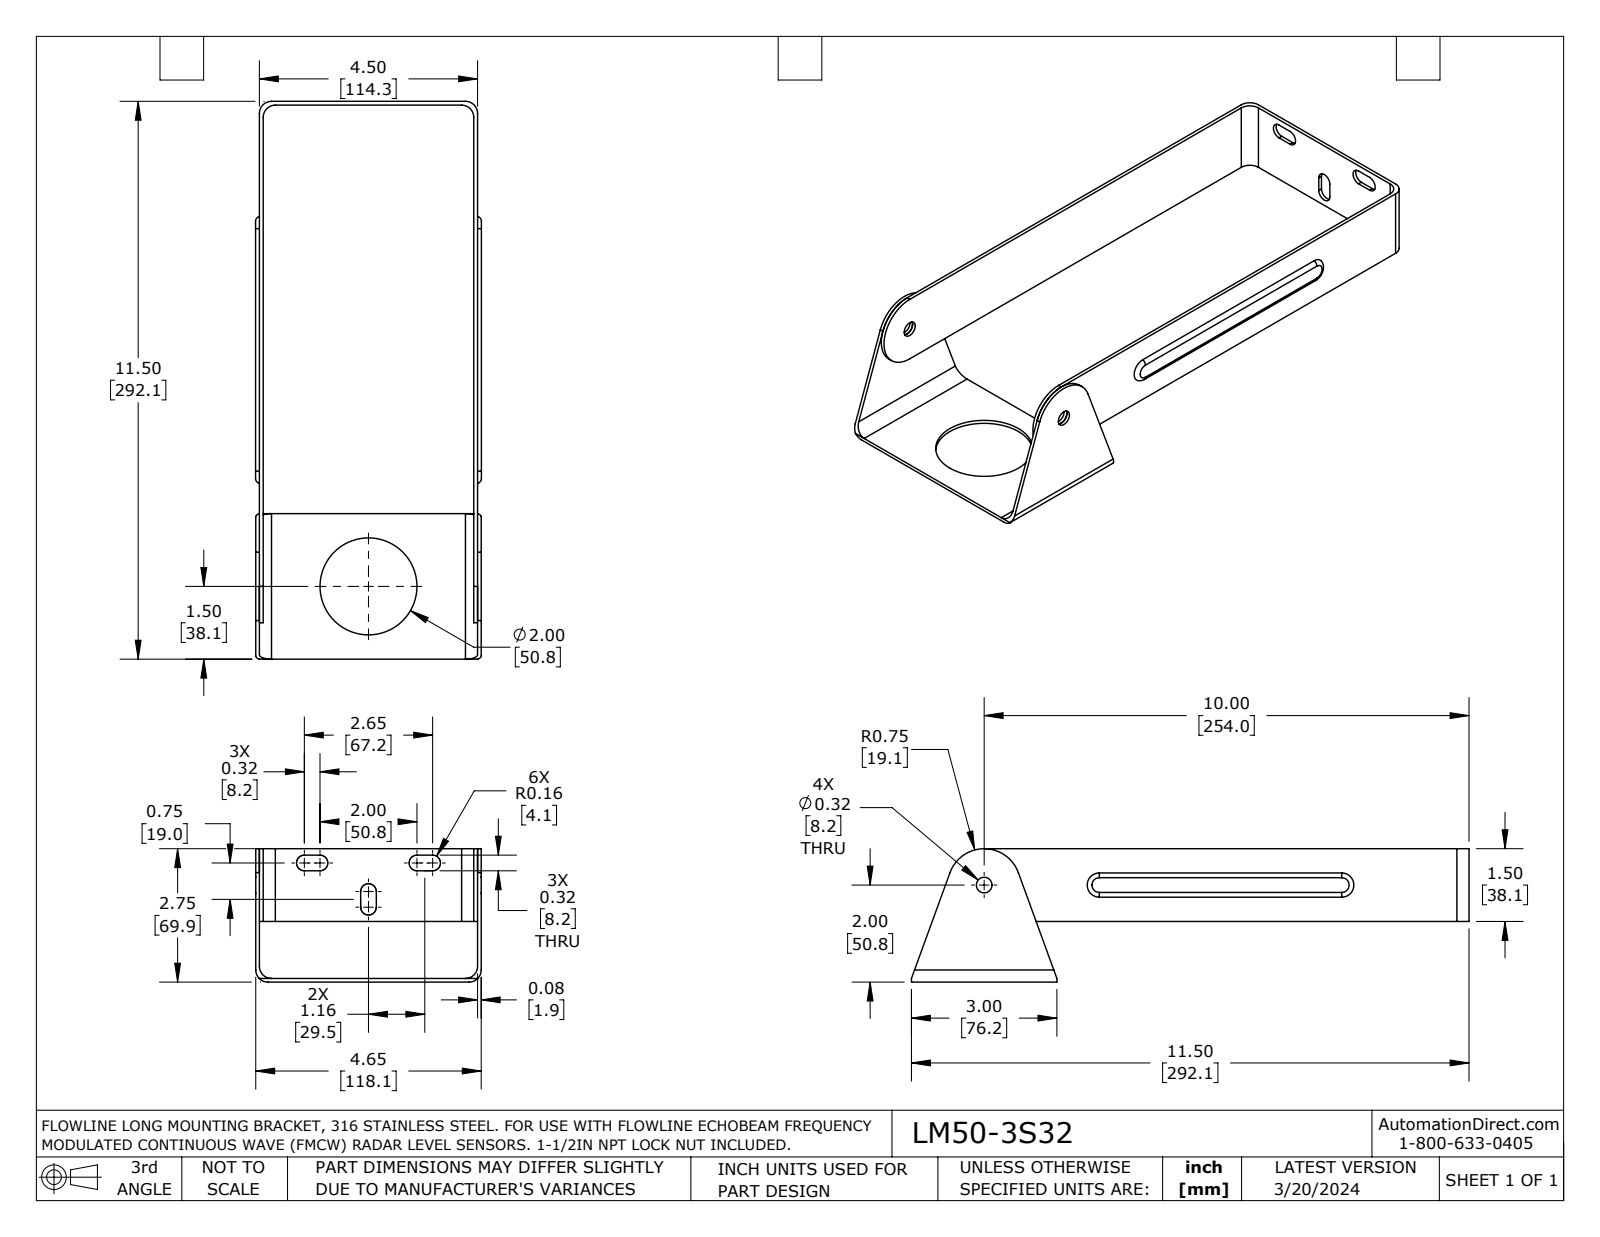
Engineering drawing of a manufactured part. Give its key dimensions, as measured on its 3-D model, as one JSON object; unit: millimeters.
{"part_name": "LM50-3S32", "step_written_by": "SolidWorks 2021 (AUTOMOTIVE_DESIGN)", "units": "millimeters", "bodies": {"solids": 2, "faces": 69, "planar": 28, "cylindrical": 35, "other": 6}, "overall_size": [292.1, 118.3, 69.9], "volume_mm3": 80820, "surface_area_mm2": 79810, "round_holes": [[8.2, 1], [50.8, 1]], "partial_cylinders_radius": [[6.4, 8], [4.1, 6], [2.5, 4], [19.1, 1]], "face_to_face_distances": [2, 112.3, 114.3, 1.9, 110.3, 3.9, 114.2, 116.2, 118.1, 4]}
